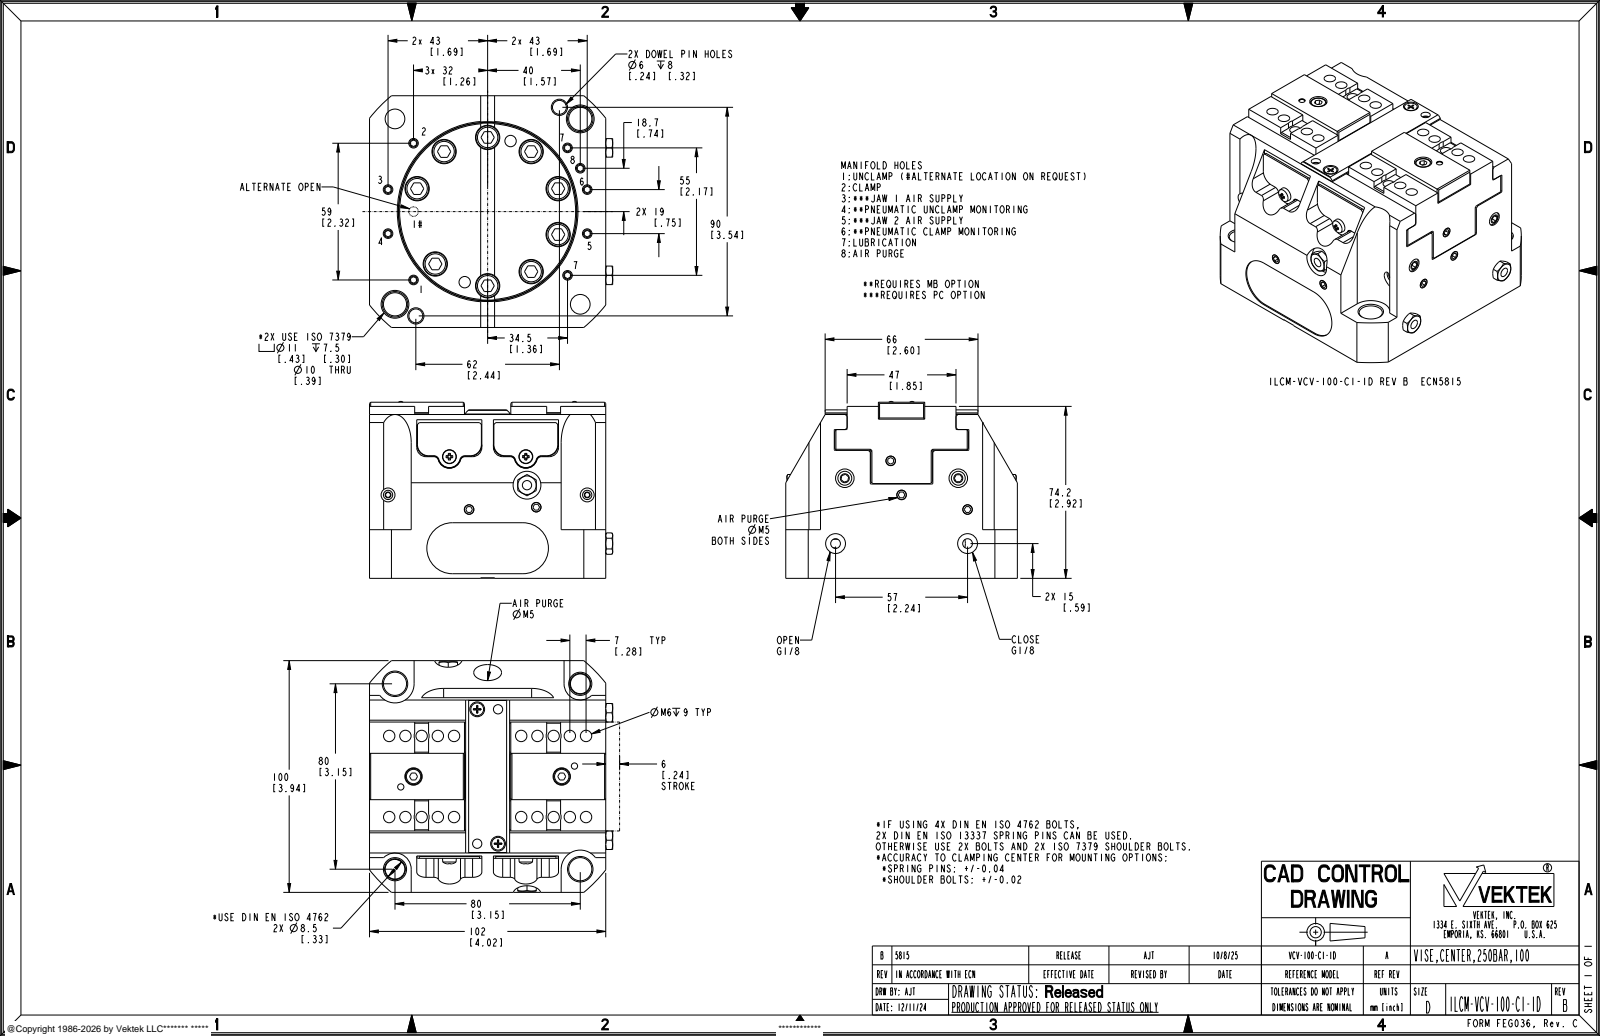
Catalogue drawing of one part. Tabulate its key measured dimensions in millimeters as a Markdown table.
| quantity | value |
| --- | --- |
| part name | DIN_915_-_M5_X_8_1; INGRASSATORE_M6X1_-_COD_D2-31-0; SFERA__X_F83_00_1; ISO_4762__-_M4_X_10_1 (+8 more) |
| STEP written by | CREO PARAMETRIC BY PTC INC, 2021164 (AUTOMOTIVE_DESIGN) |
| units | millimeters |
| bodies | 58 solids, 2033 faces (847 planar, 545 cylindrical, 641 other) |
| overall size | 105 × 100 × 76.36 |
| volume | 597 888 mm³ |
| surface area | 138 198 mm² |
| round holes (diameter × count) | 4.92 × 35, 4.13 × 18, 6.5 × 11, 3.2 × 10, 10.5 × 9, 6 × 6, 4.2 × 5, 2.4 × 4, 2.46 × 4, 3.5 × 4, 5 × 4, 9 × 3 |
| round bosses / shafts (diameter × count) | 5 × 18, 10 × 9, 6 × 9, 6.3 × 4, 4 × 4, 3 × 4, 7 × 2, 5.5 × 2 |
| partial cylindrical surfaces (radius × count) | 0.4 × 12, 4 × 12, 2 × 8, 5 × 6, 2.6 × 4, 3.25 × 4, 3.6 × 4, 1.25 × 2 |
| main face-to-face distances | 9.3, 55.2, 45.9, 13.5, 102, 2, 10, 23.5, 23.3, 33.5 |
| hole center spacings | 32, 37.62, 64, 15.03, 32.53, 35.95, 40.86, 44.04 |
